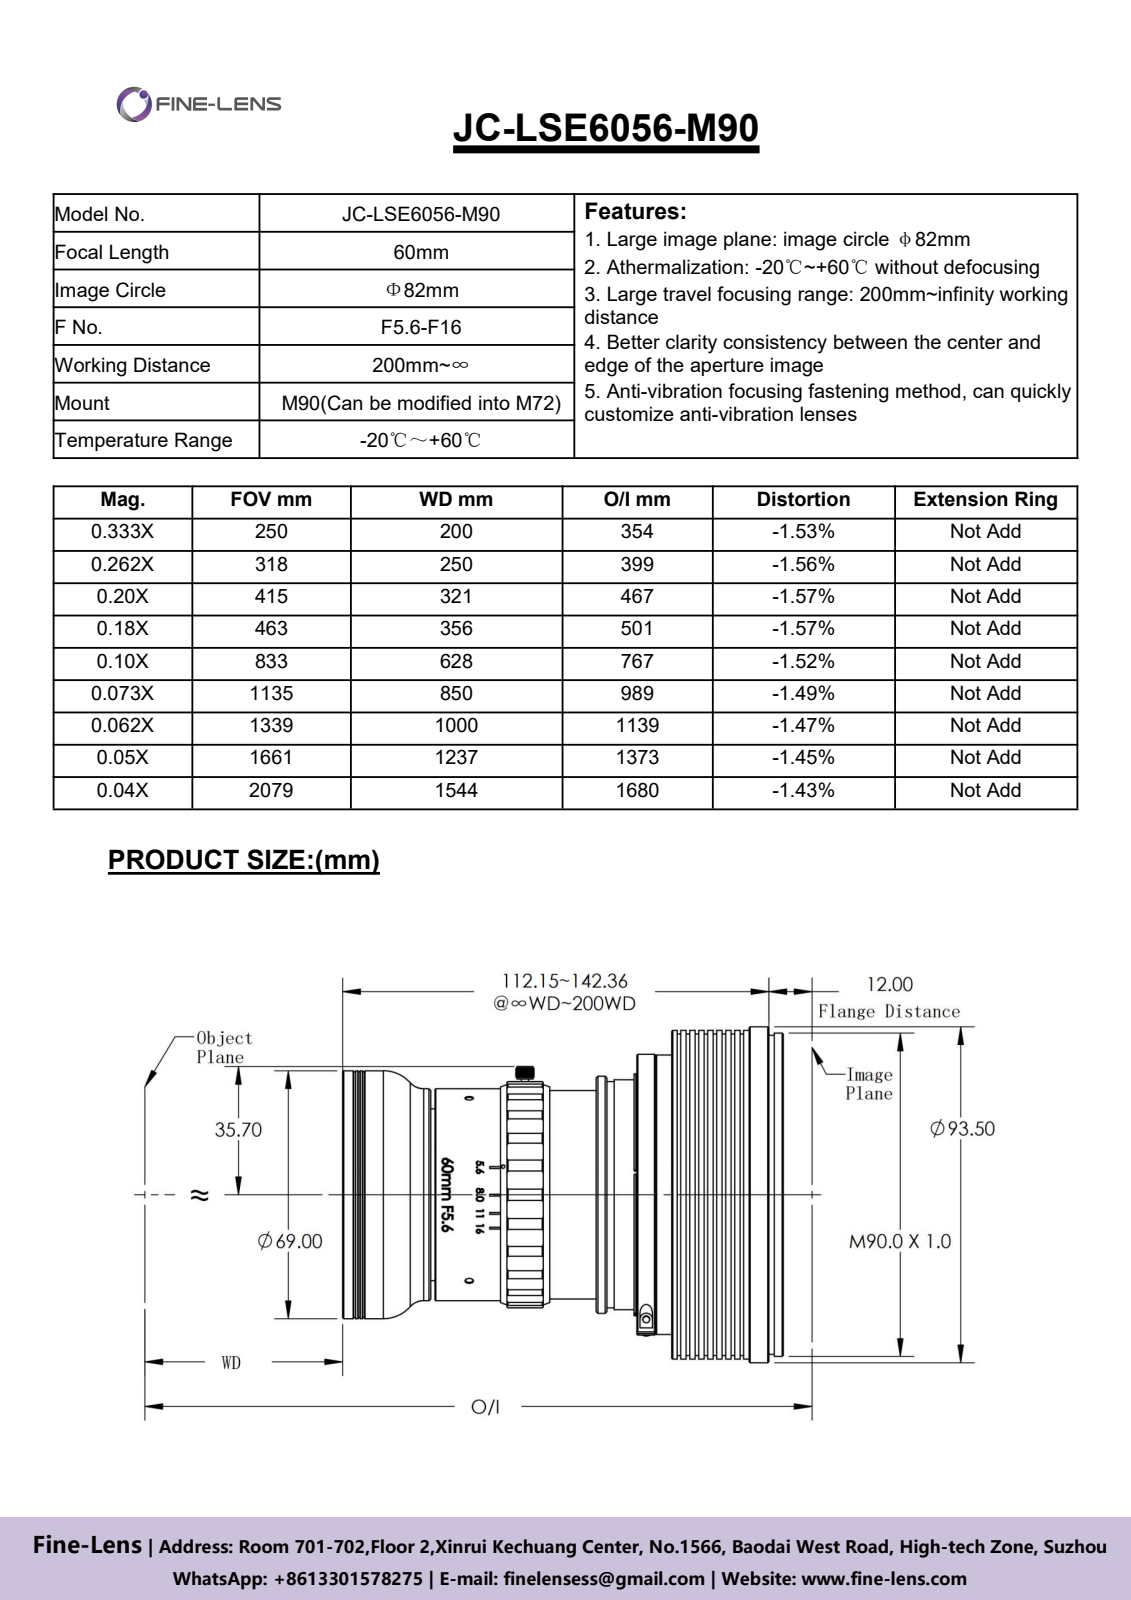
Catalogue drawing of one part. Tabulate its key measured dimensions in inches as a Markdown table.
| quantity | value |
| --- | --- |
| STEP written by | SolidWorks 2018 (CONFIG_CONTROL_DESIGN) |
| units | inches |
| bodies | 1 solid, 133 faces (35 planar, 62 cylindrical, 36 other) |
| overall size | 4.823 × 3.681 × 3.681 |
| volume | 30.38 in³ |
| surface area | 77.86 in² |
| round bosses / shafts (diameter × count) | 3.681 × 1, 3.602 × 1, 3.543 × 1, 3.524 × 1, 3.496 × 1, 3.077 × 1, 3.063 × 1, 2.717 × 1 |
| main face-to-face distances | 4.823, 0.098, 0.197, 3.603, 1.22, 0.295, 0.394, 3.221, 0.382, 1.602 |
